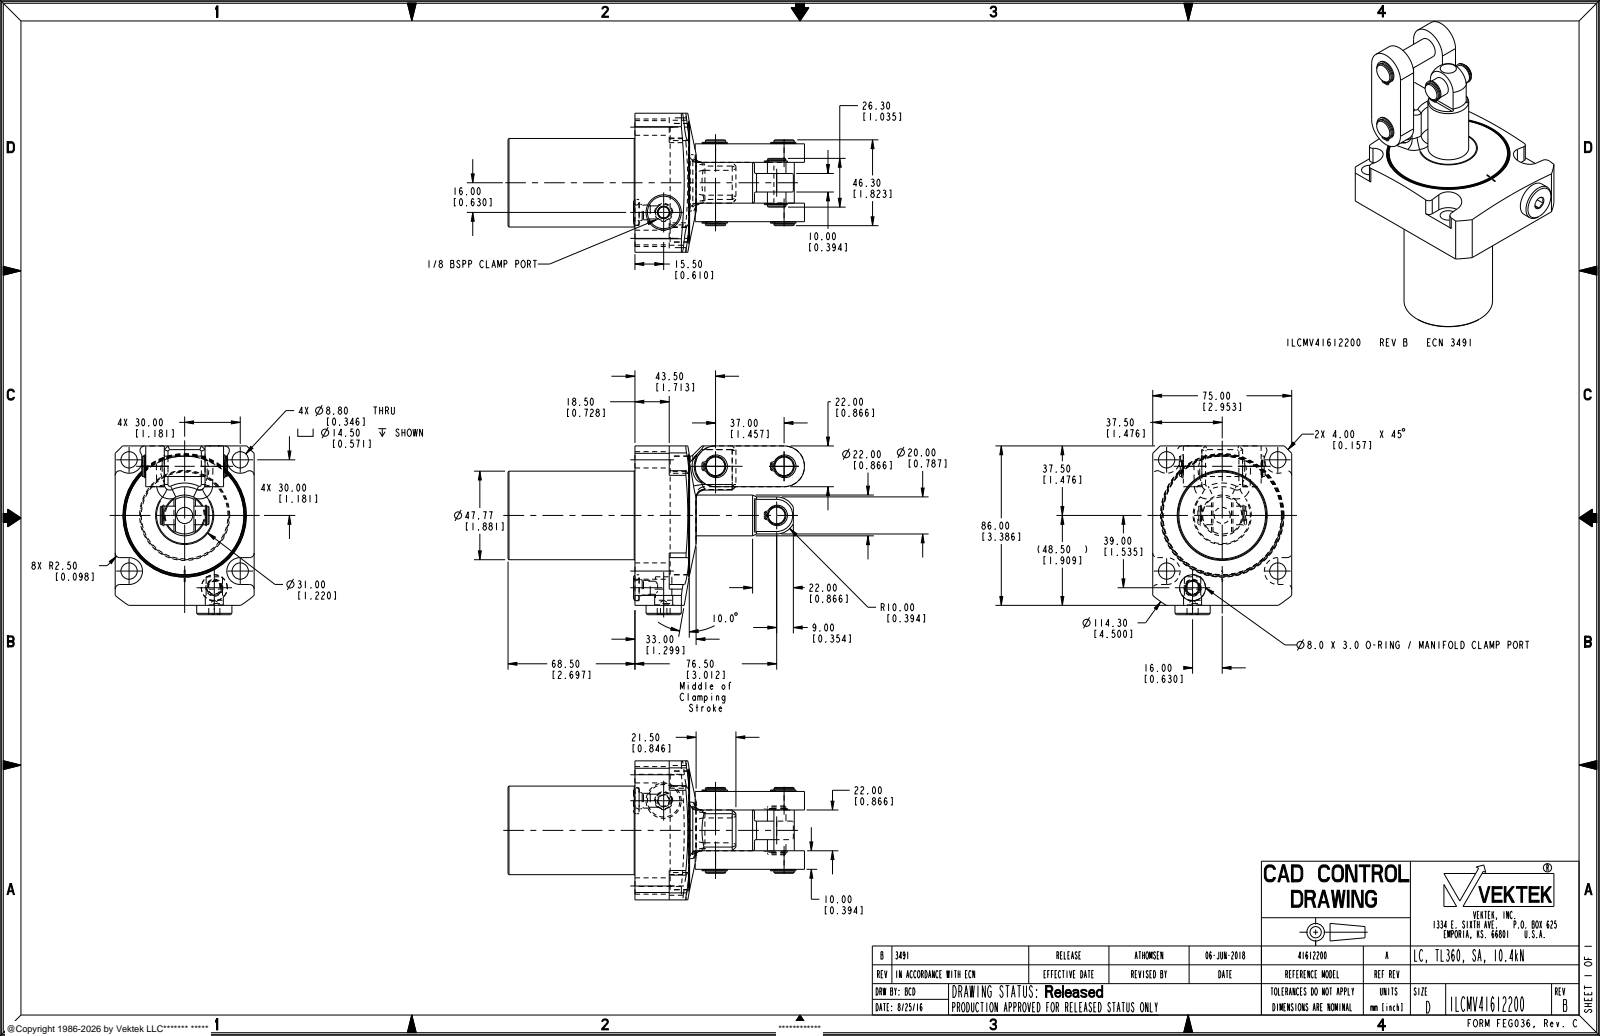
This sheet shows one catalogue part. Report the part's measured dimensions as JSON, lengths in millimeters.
{"part_name": "ILCMV41612200_BODY; ILCMV41612200_LUG; ILCMV41612200", "step_written_by": "PRO/ENGINEER BY PARAMETRIC TECHNOLOGY CORPORATION, 2013320 (AUTOMOTIVE_DESIGN)", "units": "millimeters", "bodies": {"solids": 3, "faces": 337, "planar": 118, "cylindrical": 149, "other": 70}, "overall_size": [160, 91.05, 75], "volume_mm3": 356536, "surface_area_mm2": 59303, "round_holes": [[1.04, 6], [8.8, 4], [7.04, 1], [8.84, 1], [14, 1], [64.03, 1]], "round_bosses_or_shafts": [[12.23, 2], [11, 2], [10.46, 2], [63.93, 1], [47.77, 1], [22, 1], [19, 1], [11.06, 1]], "partial_cylinders_radius": [[2.5, 8], [1.04, 6], [0.8, 4], [1.57, 4], [7.25, 4], [1.46, 2], [3, 2], [11, 2]], "face_to_face_distances": [19, 10, 16.5, 58.5, 75, 68.5, 87.5, 26.5, 48.5, 32], "hole_center_spacings": [42.43, 60, 2.6, 37, 37.09, 84.85, 2.34, 16.64]}
